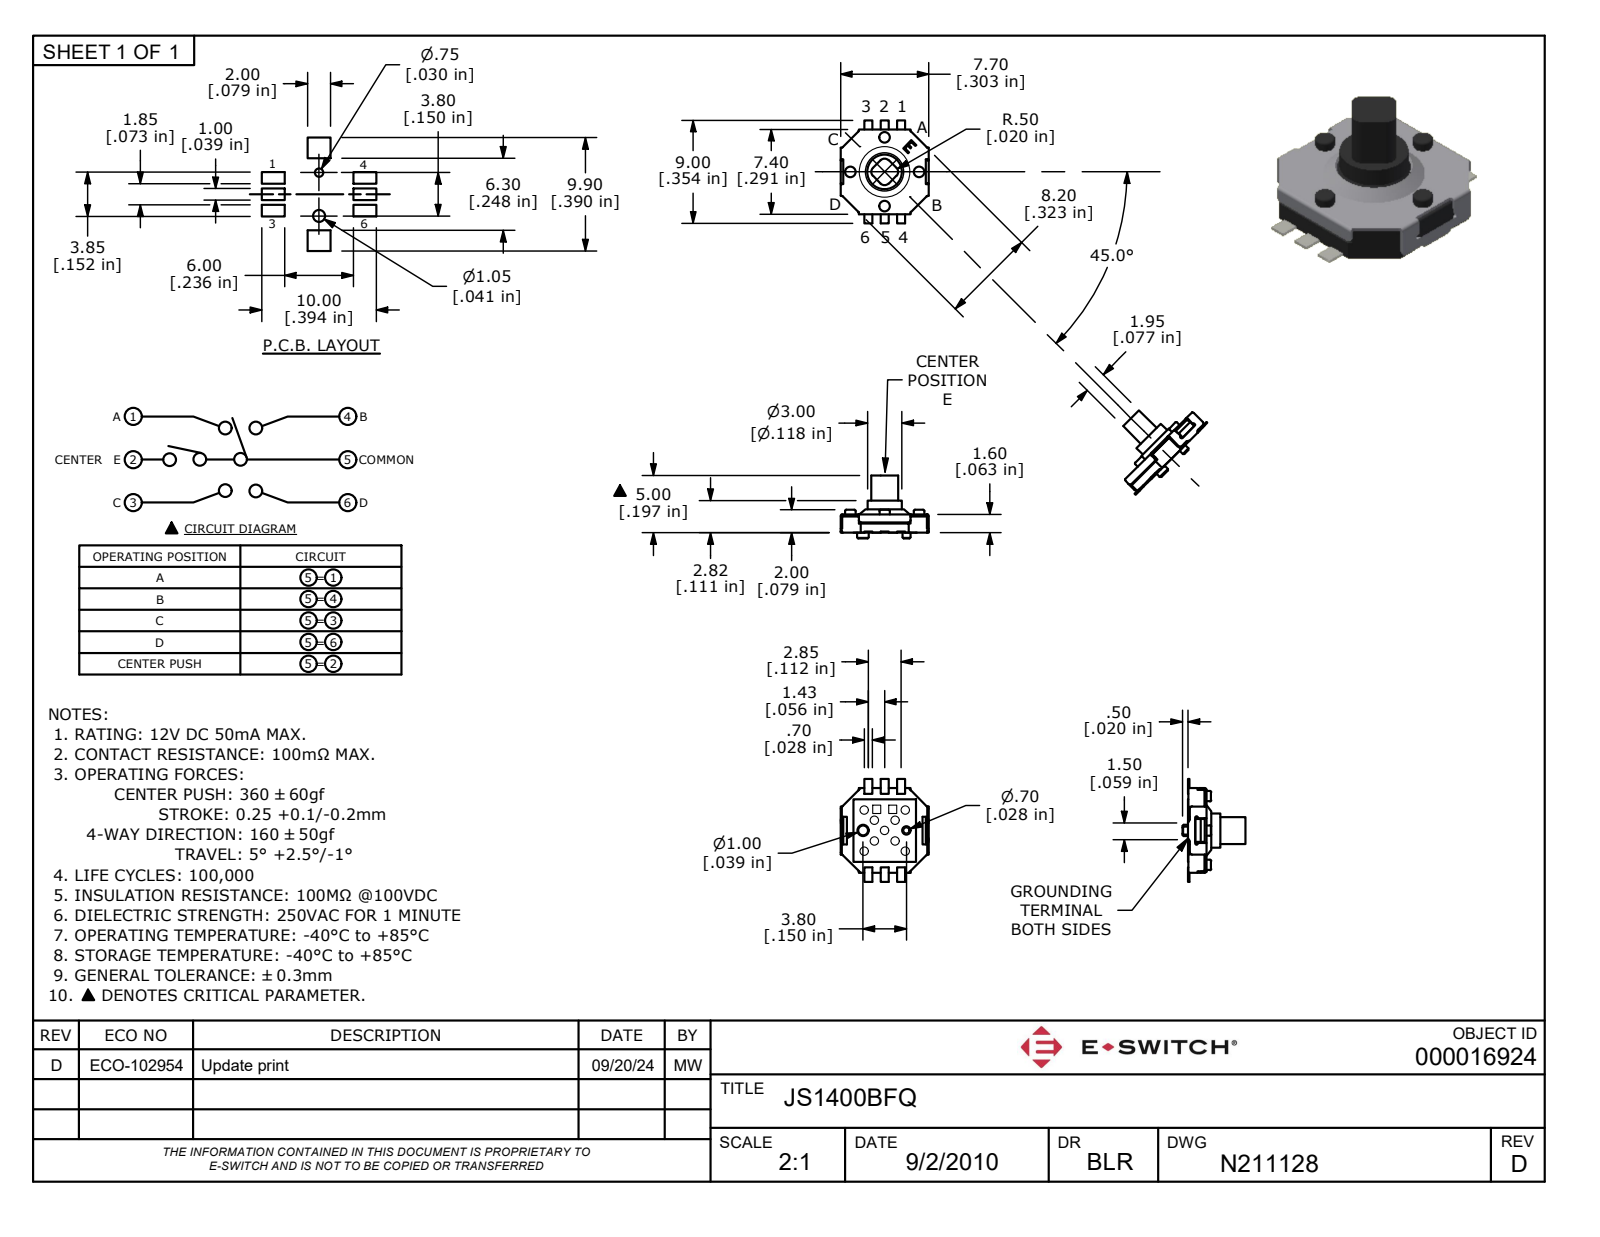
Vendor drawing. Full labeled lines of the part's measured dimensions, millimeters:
Part name (STEP PRODUCT): P:\\E-Switch Secure\\3D_MODELS_STP_FORMAT\\JS1400BFQ.stp
STEP written by: ACIS (CONFIG_CONTROL_DESIGN)
Units: millimetres
Bodies: 2 solids, 247 faces (193 planar, 44 cylindrical, 10 other)
Overall size (bounding box): 9 × 7.8 × 5.5
Volume: 80 mm³ · Surface area: 330 mm²
Round holes (diameter × count): ⌀0.7 ×9, ⌀0.8 ×4
Round bosses / shafts (diameter × count): ⌀0.7 ×5, ⌀0.9 ×4, ⌀3 ×1, ⌀1 ×1
Partial cylindrical surfaces — rounded edges, fillets, slot ends (radius × count): R0.5 ×4, R1.2 ×4
Main face-to-face distances: 0.6, 1, 1.6, 0.4, 0.9, 0.7, 1.4, 0.9, 0.5, 1.6
Hole centre spacings: 1.3, 2.2, 2.3, 2.8, 4, 5.1, 2.5, 1.8
